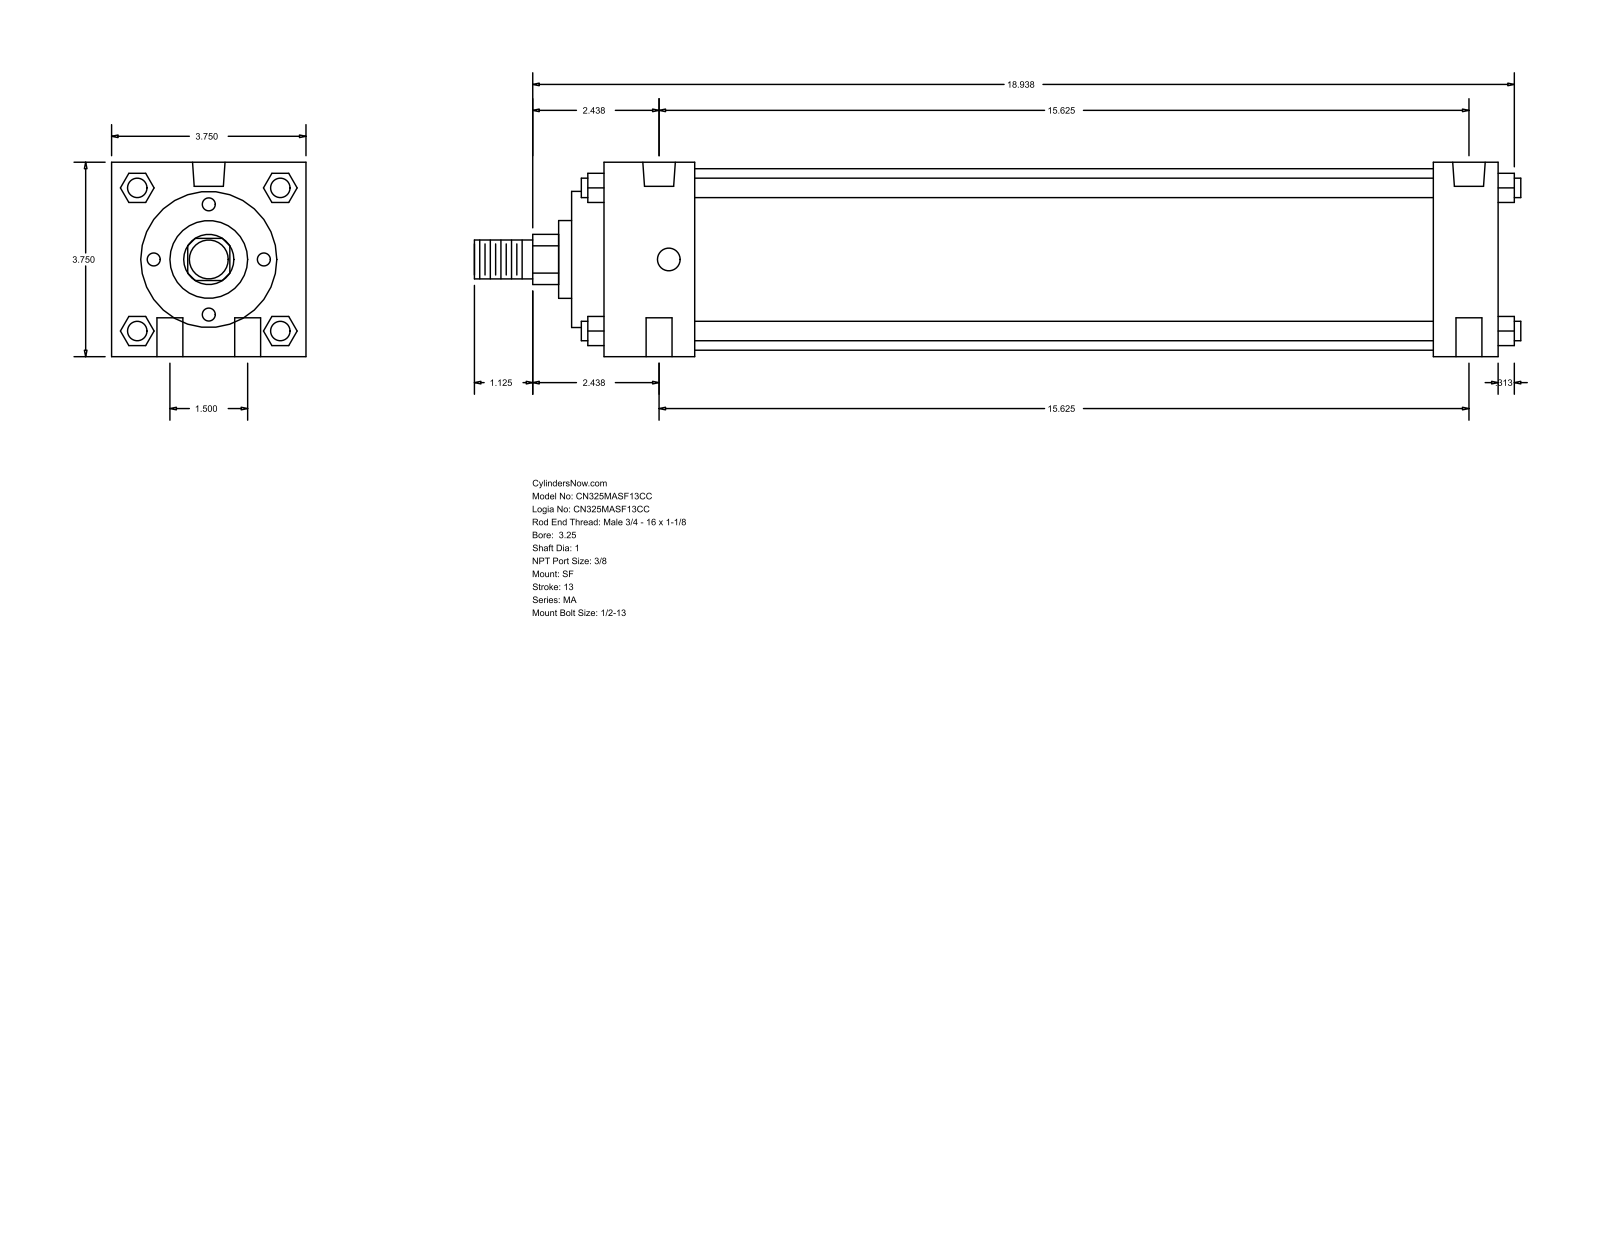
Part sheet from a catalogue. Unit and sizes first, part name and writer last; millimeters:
Units: millimetres
Overall size (bounding box): 512.76 × 95.25 × 95.25
Round holes (diameter × count): ⌀12.7 ×4, ⌀11.11 ×2, ⌀15.93 ×2
Round bosses / shafts (diameter × count): ⌀9.53 ×4, ⌀88.9 ×1, ⌀66.67 ×1, ⌀38.1 ×1, ⌀25.4 ×1, ⌀19.05 ×1
Partial cylindrical surfaces — rounded edges, fillets, slot ends (radius × count): R12.29 ×1
Main face-to-face distances: 95.24, 438.15, 454.02, 406.4, 31.75, 44.46, 361.94, 393.69, 15.87, 60.33
Hole centre spacings: 19.05, 397.34, 396.88, 38.1, 398.7, 387.35
Bodies: 0 solids, 126 faces (95 planar, 31 cylindrical, 0 other)
Part name (STEP PRODUCT): MA_SF__0325_1
STEP written by: GSSL Pune (CONFIG_CONTROL_DESIGN)
